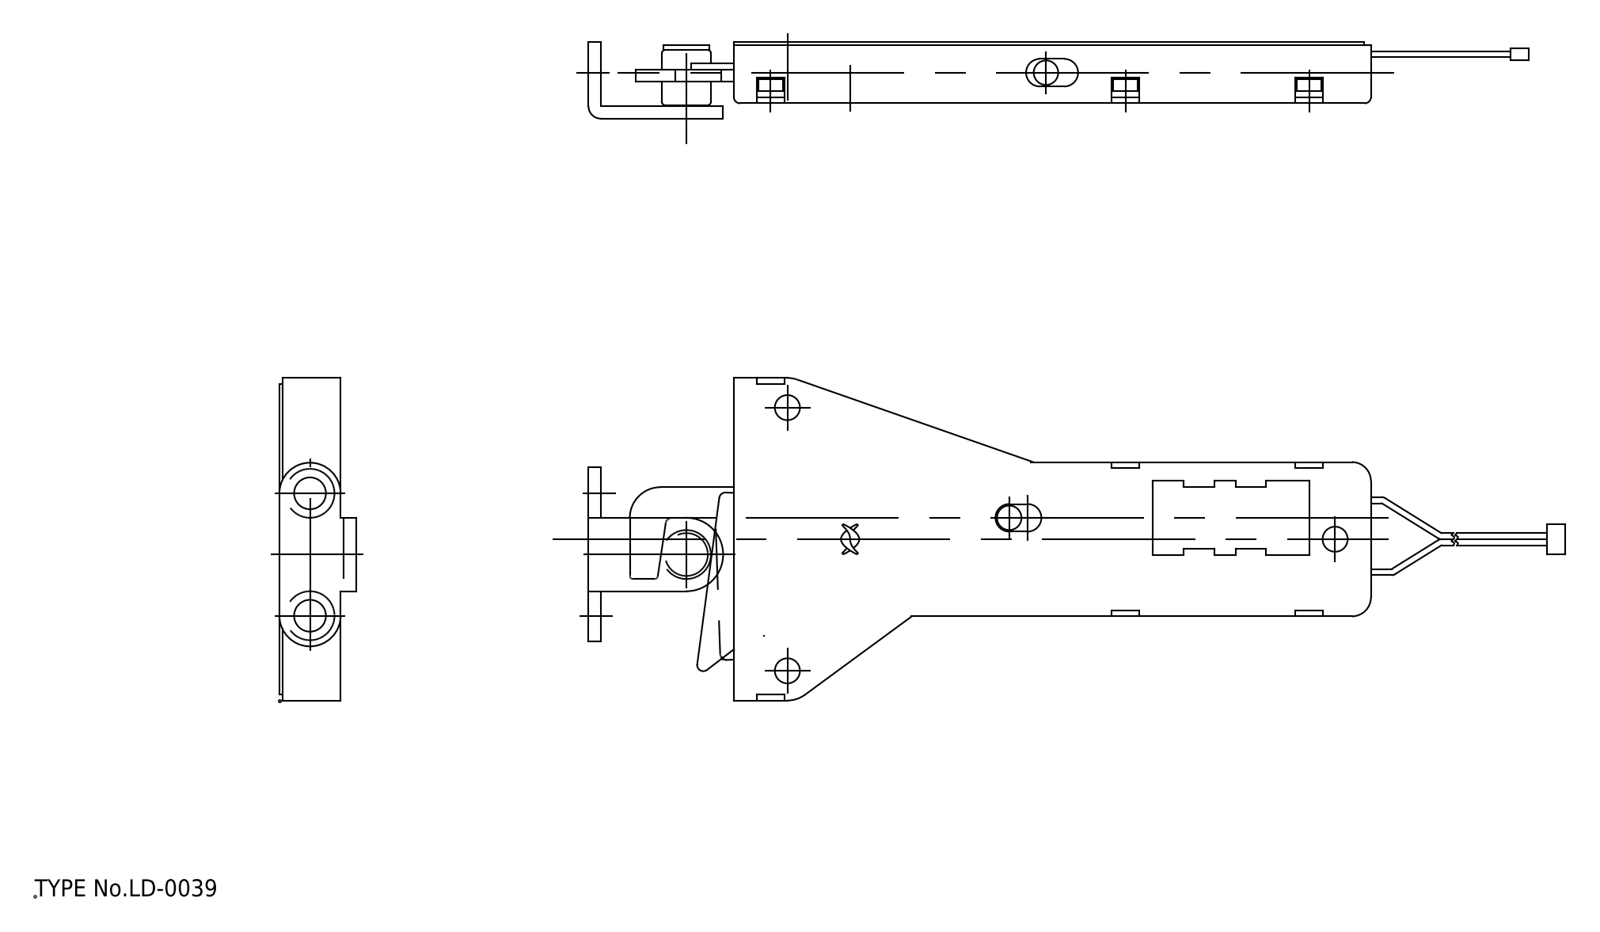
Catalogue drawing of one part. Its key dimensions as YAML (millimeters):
part_name: "カバー; キーパー; 本体_mr; ロック_mr (+1 more)"
step_written_by: "spGate 16.7.1 (AUTOMOTIVE_DESIGN)"
units: millimeters
bodies: {solids: 5, faces: 174, planar: 98, cylindrical: 70, other: 6}
overall_size: [127.85, 52.7, 13]
volume: 24158
surface_area: 25408
round_holes:
  - {diameter: 3.5, count: 3}
  - {diameter: 4.1, count: 3}
  - {diameter: 5.2, count: 2}
  - {diameter: 2.5, count: 1}
  - {diameter: 6.1, count: 1}
round_bosses_or_shafts:
  - {diameter: 10, count: 1}
  - {diameter: 8, count: 1}
  - {diameter: 6, count: 1}
partial_cylinders:
  - {radius: 1, count: 9}
  - {radius: 0.5, count: 7}
  - {radius: 2.25, count: 4}
  - {radius: 5, count: 3}
  - {radius: 2, count: 2}
  - {radius: 6, count: 2}
  - {radius: 2.5, count: 1}
  - {radius: 3.75, count: 1}
face_to_face_distances: [1, 9, 10, 1.1, 8, 2, 3.6, 5.4, 4.4, 24.1]
hole_center_spacings: [92.05, 20, 20.71, 27.02, 43, 79.33]
